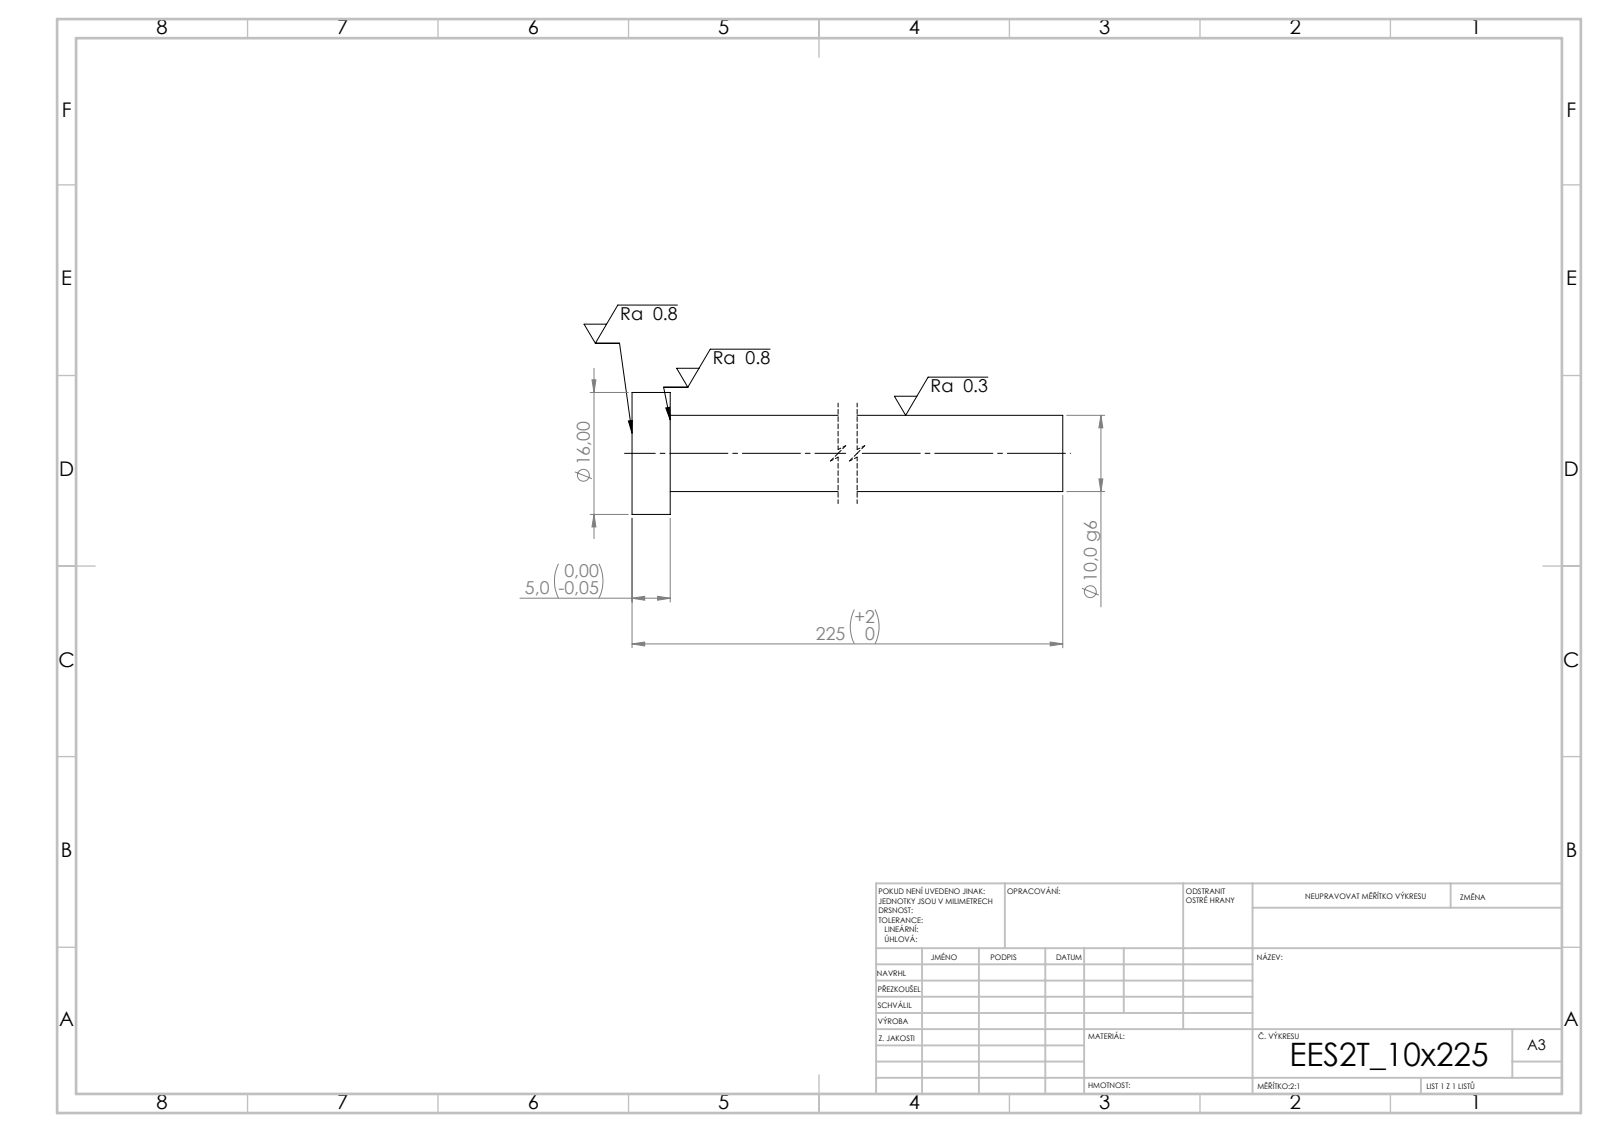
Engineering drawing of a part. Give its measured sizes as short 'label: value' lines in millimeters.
written by: SolidWorks 2019 (CONFIG_CONTROL_DESIGN)
unit: mm
bodies: 1 solid, 7 faces (3 planar, 4 cylindrical, 0 other)
size: 225 × 16 × 16
volume: 18 284 mm³; area: 7 565 mm²
bosses: 1× ⌀16, 1× ⌀10
face distances: 5, 225, 220
